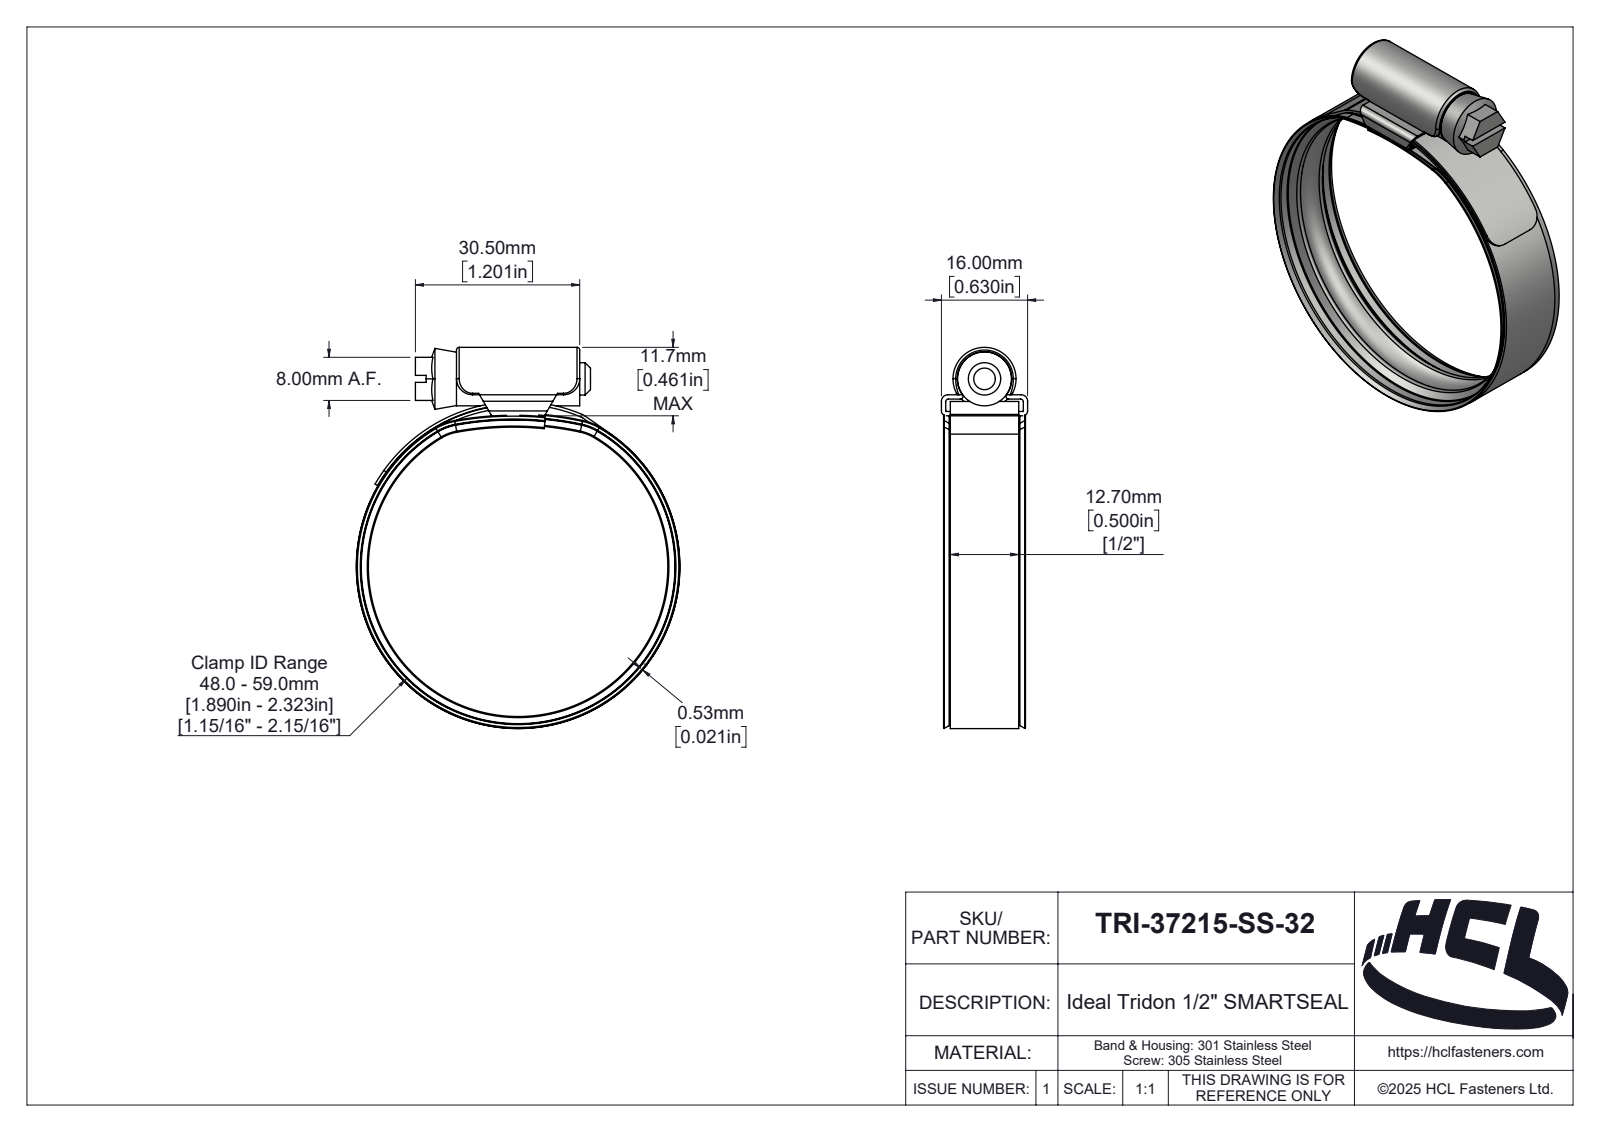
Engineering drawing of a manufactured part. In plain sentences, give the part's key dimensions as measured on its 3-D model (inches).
The part is named "TRI-37215-SS-32". Its 3-D file was written by "SolidWorks 2025 (AUTOMOTIVE_DESIGN)". It is 4 solids with 418 faces: 42 planar, 119 cylindrical and 257 other. Overall it measures 2.785 by 2.365 by 0.63 inches. Its volume is 0.316 cubic inches and its surface area 23.71 square inches. Round holes: 1 of diameter 2.299, 1 of diameter 2.323. Round bosses or shafts: 1 of diameter 2.365, 1 of diameter 2.315, 1 of diameter 0.394, 1 of diameter 0.236. Partial cylindrical surfaces (rounded edges, fillets, slot ends): 6 of radius 0.02, 4 of radius 0.118, 2 of radius 0.004, 2 of radius 0.035, 2 of radius 0.047, 2 of radius 0.39, 2 of radius 0.398, 1 of radius 0.018. The main face-to-face distances are 0.031, 0.122, 0.5, 0.091, 0.021, 1.201, 0.154, 0.065, 0.565, 0.598.
